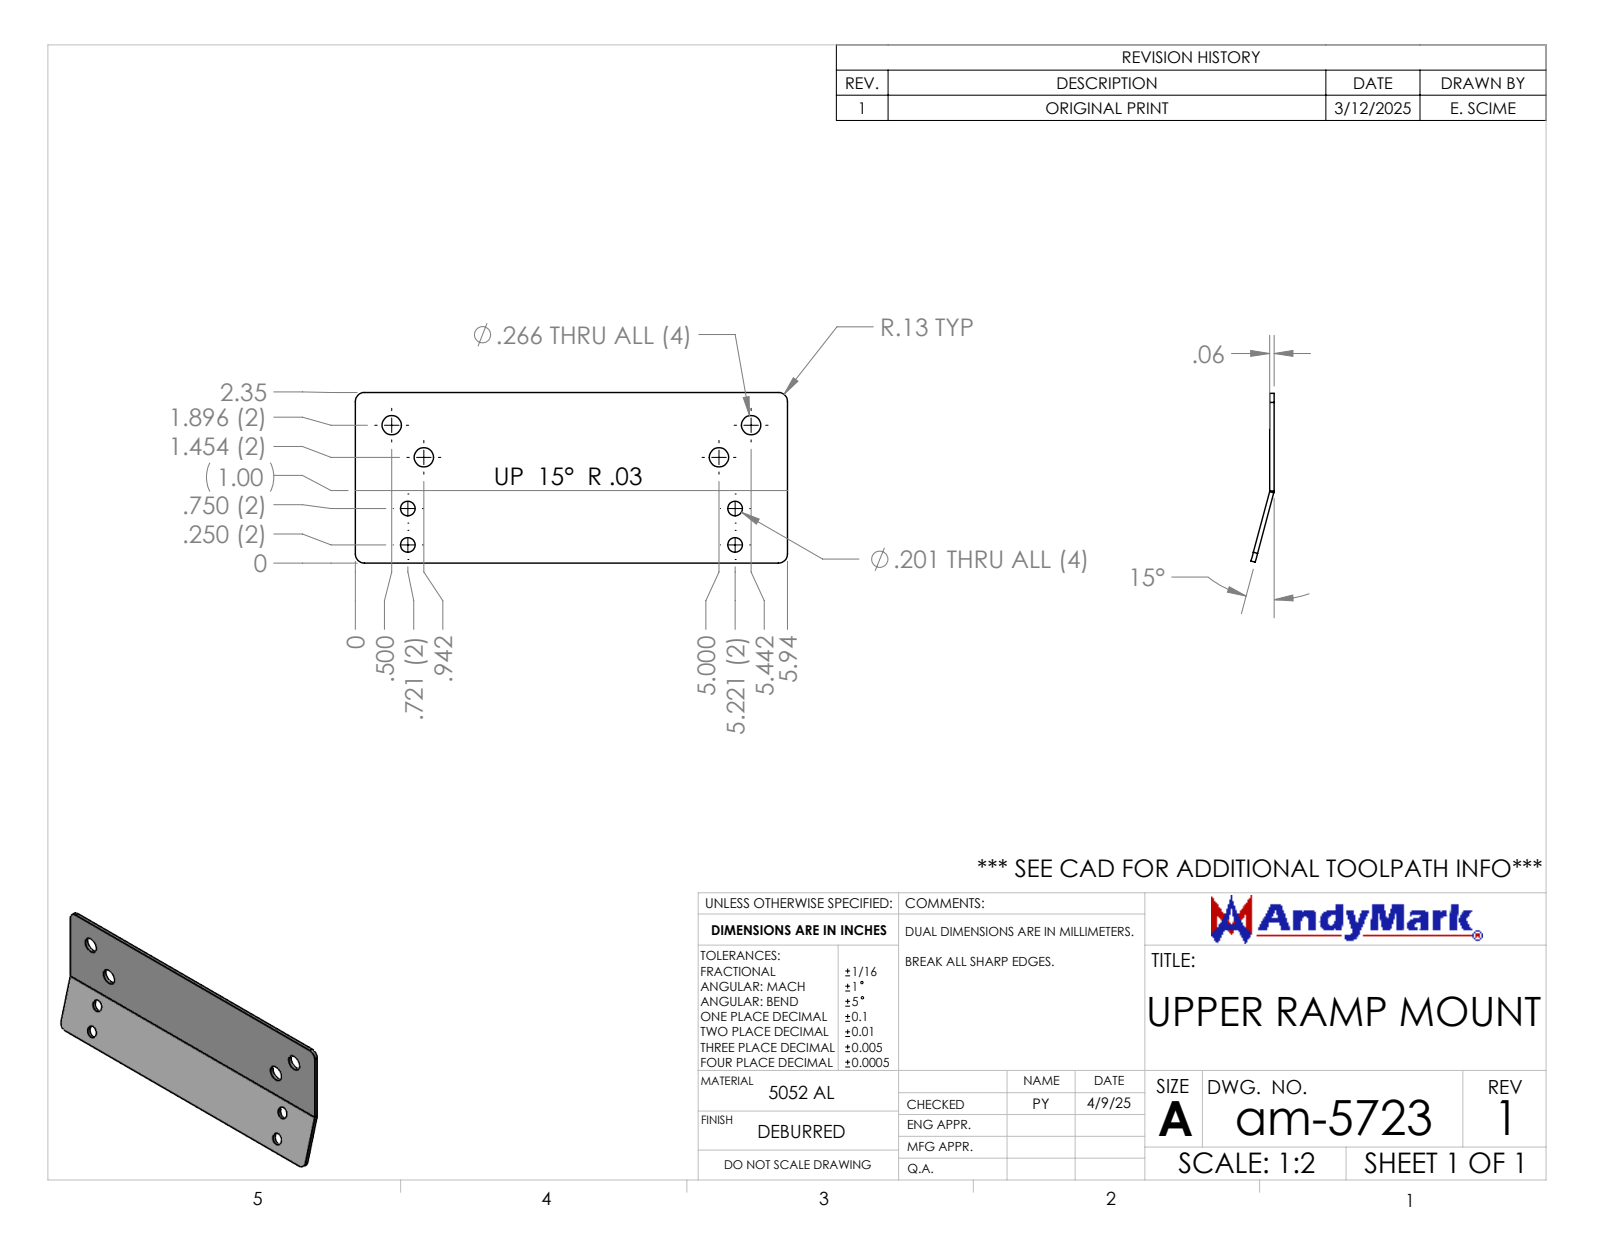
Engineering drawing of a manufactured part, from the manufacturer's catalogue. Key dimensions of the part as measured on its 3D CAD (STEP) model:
Part name (STEP PRODUCT): am-5723 Upper Ramp Mount
STEP written by: SolidWorks 2024 (AUTOMOTIVE_DESIGN)
Units: inches
Bodies: 1 solid, 34 faces (12 planar, 22 cylindrical, 0 other)
Overall size (bounding box): 5.942 × 2.32 × 0.317
Volume: 0.815 in³ · Surface area: 28.48 in²
Round holes (diameter × count): ⌀0.201 ×4, ⌀0.266 ×4
Partial cylindrical surfaces — rounded edges, fillets, slot ends (radius × count): R0.125 ×4, R0.029 ×1, R0.089 ×1
Main face-to-face distances: 0.06, 5.942
Hole centre spacings: 0.5, 0.625, 4.5, 4.522, 4.528, 4.058, 4.942
